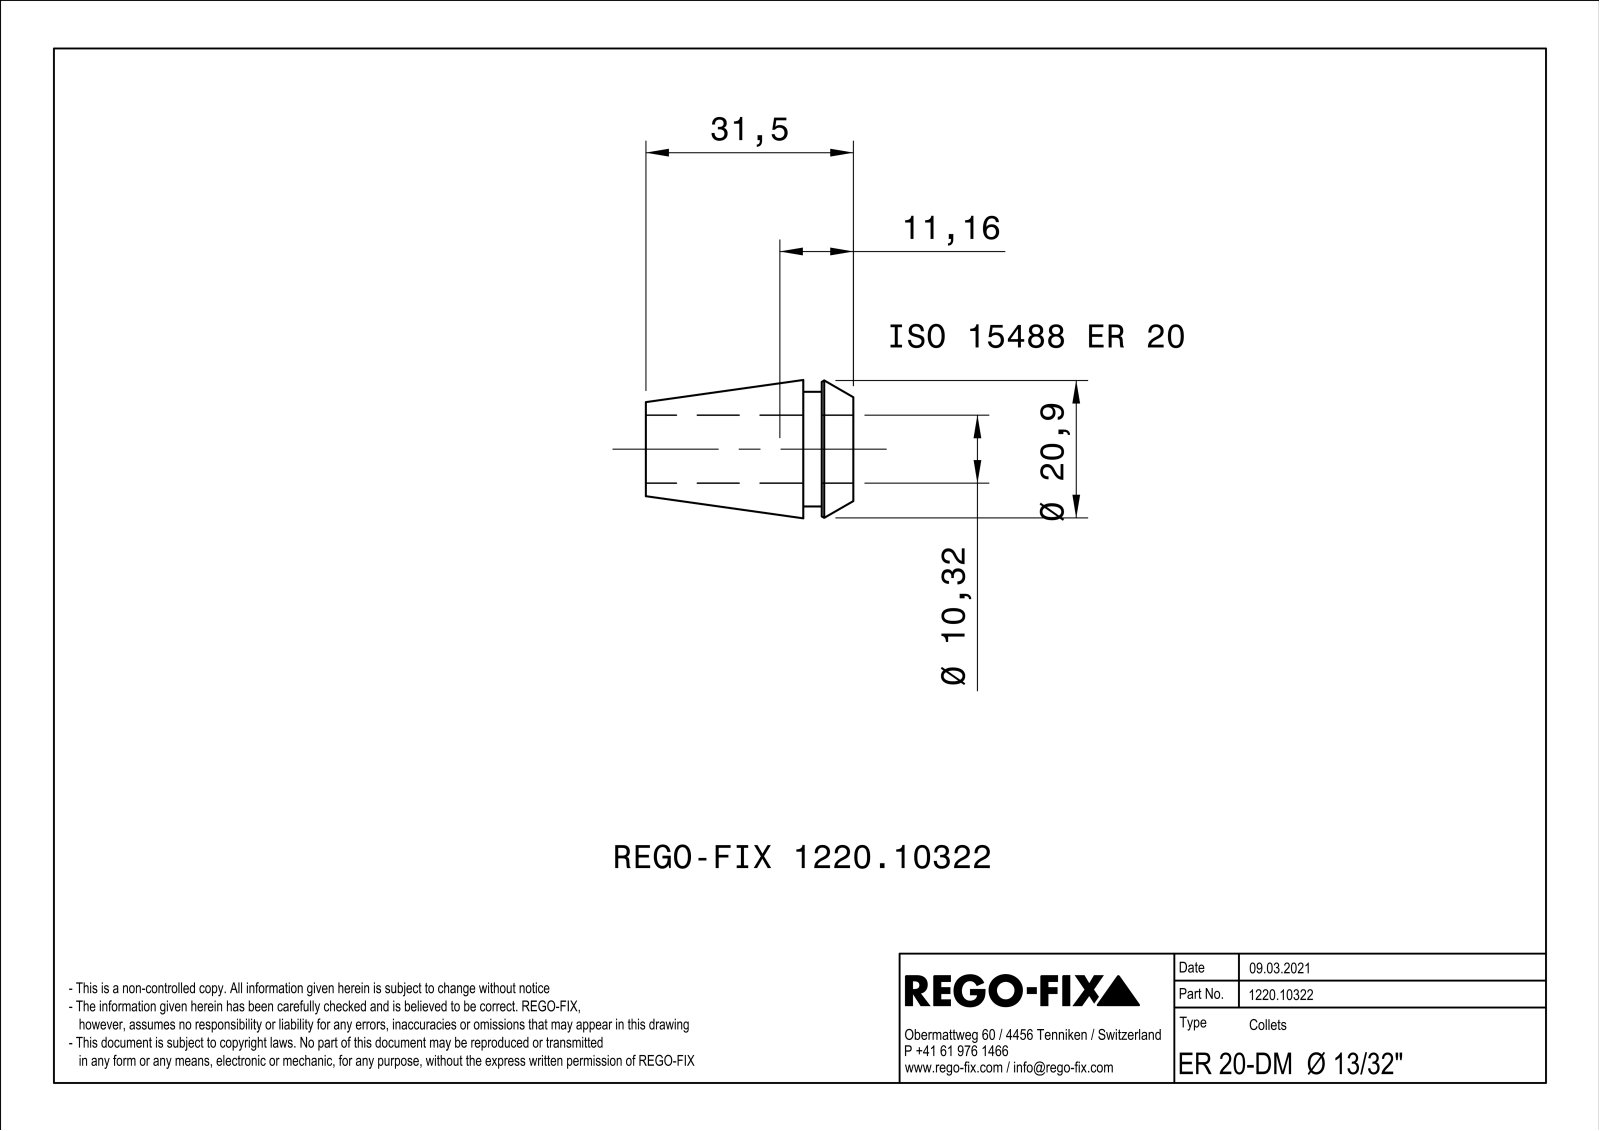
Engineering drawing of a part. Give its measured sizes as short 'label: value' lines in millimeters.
name: NOCUT
written by: SIEMENS PLM Software Solid Edge ST10 (AUTOMOTIVE_DESIGN)
unit: mm
bodies: 1 solid, 154 faces (80 planar, 9 cylindrical, 65 other)
size: 31.5 × 20.98 × 20.98
volume: 4 207 mm³; area: 5 216 mm²
holes: 1× ⌀10.32
bosses: 1× ⌀17.4
face distances: 0.8, 7.6, 4.8, 2.8, 31.5, 26.7, 23.9, 14, 9.2, 6.4
